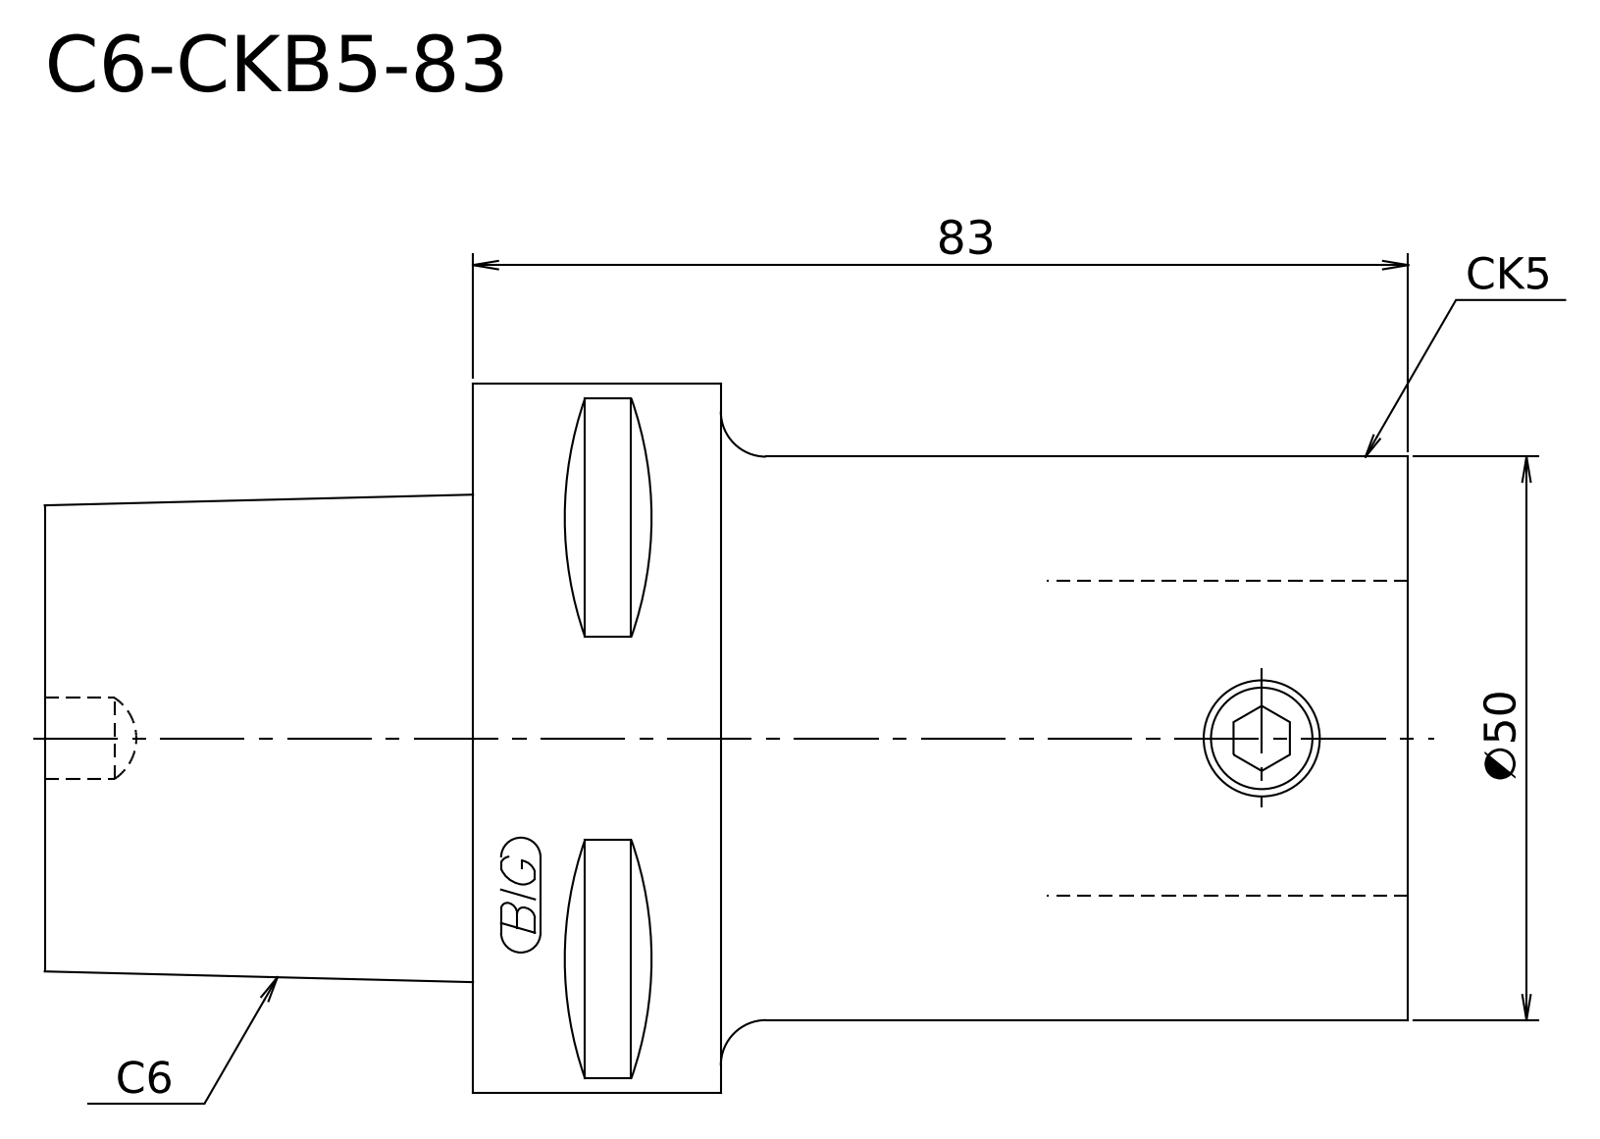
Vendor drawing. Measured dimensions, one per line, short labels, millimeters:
written by: Kubotek KeyCreator V8.5.1 (14335) (CONFIG_CONTROL_DESIGN)
unit: mm
bodies: 1 solid, 10 faces (4 planar, 2 cylindrical, 4 other)
size: 121 × 62.98 × 62.98
volume: 244 428 mm³; area: 24 849 mm²
bosses: 1× ⌀62.98, 1× ⌀50
face distances: 83, 121, 38, 61, 22, 60
